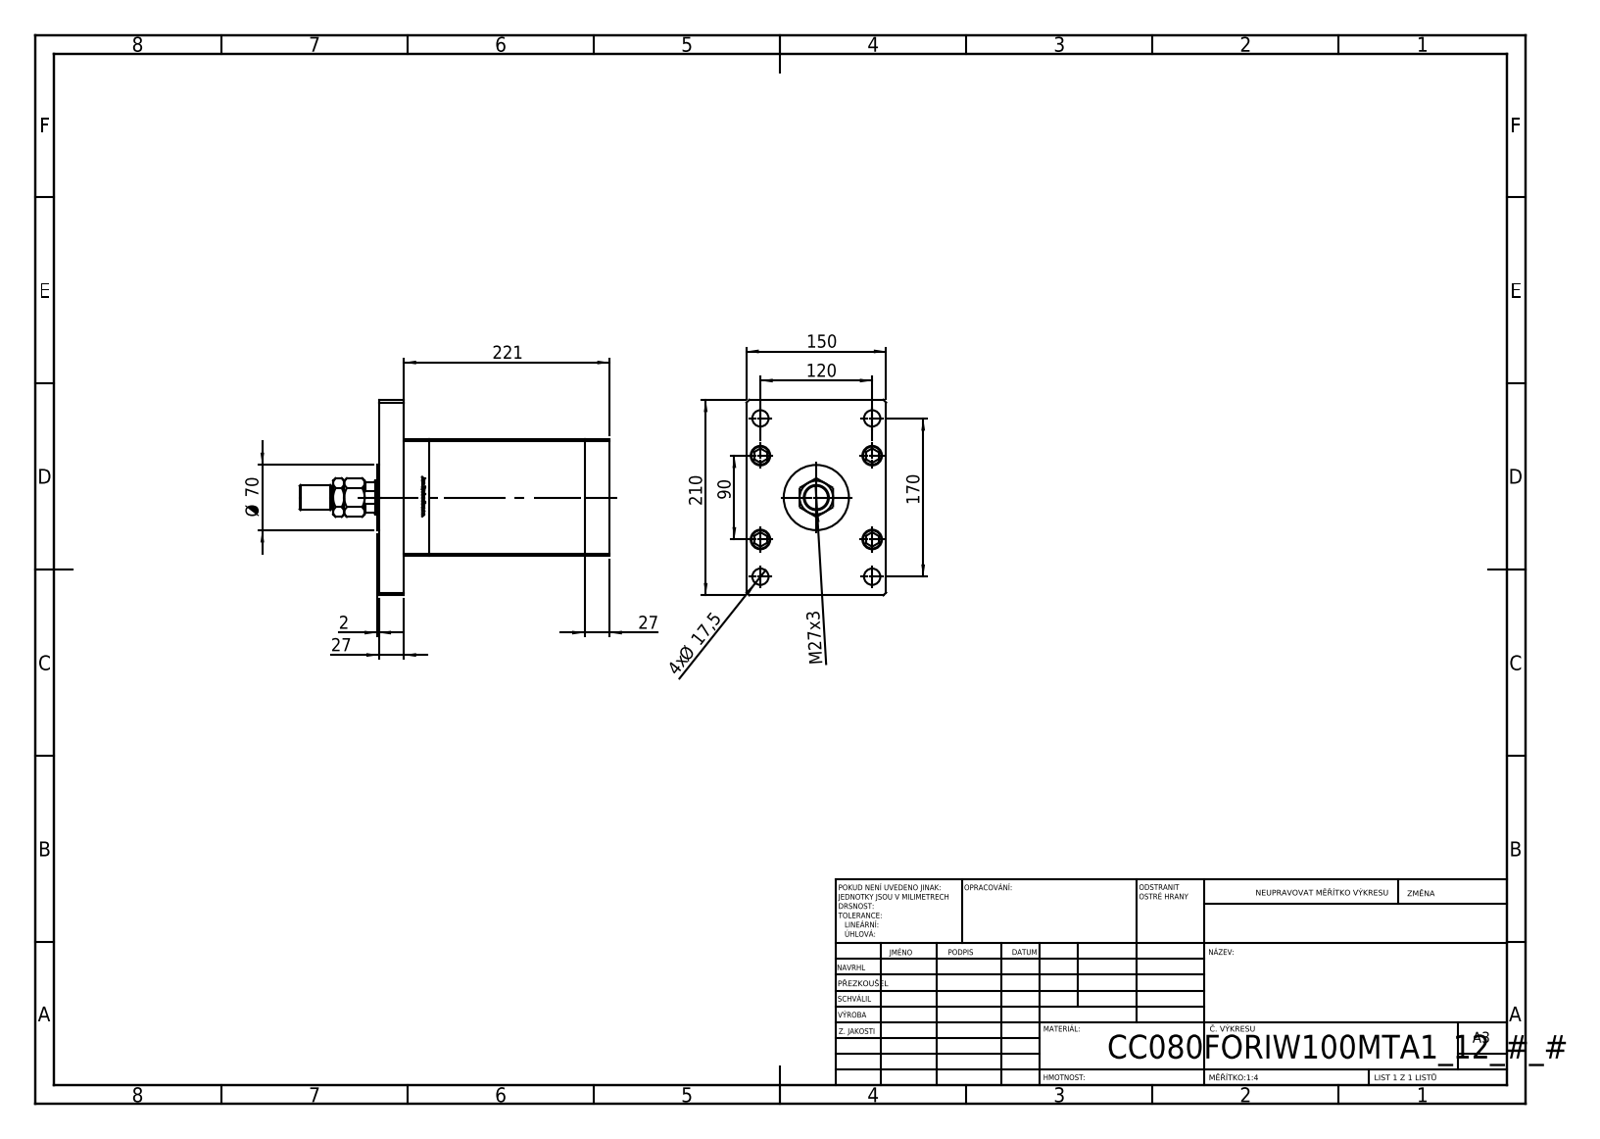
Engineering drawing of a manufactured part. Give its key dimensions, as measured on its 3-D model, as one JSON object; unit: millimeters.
{"part_name": "V220C_F; V220C_F_MIDDLE; V220C BACK_F; V220C_VC_F (+3 more)", "step_written_by": "SolidWorks 2019 (CONFIG_CONTROL_DESIGN)", "units": "millimeters", "bodies": {"solids": 20, "faces": 1347, "planar": 528, "cylindrical": 183, "other": 636}, "overall_size": [333, 210, 150], "volume_mm3": 4425000, "surface_area_mm2": 480255, "round_holes": [[17.5, 9], [22, 5], [16, 4], [21, 4], [25.5, 1], [36, 1], [37.5, 1]], "round_bosses_or_shafts": [[8, 9], [21, 5], [80, 1], [70, 1], [27, 1], [25, 1]], "partial_cylinders_radius": [[0.93, 2], [17.5, 1]], "face_to_face_distances": [27, 194, 221, 150, 125, 167, 54, 248, 33.5, 6.5], "hole_center_spacings": [51, 40, 75, 104.04, 120, 126.49, 130, 176.92]}
